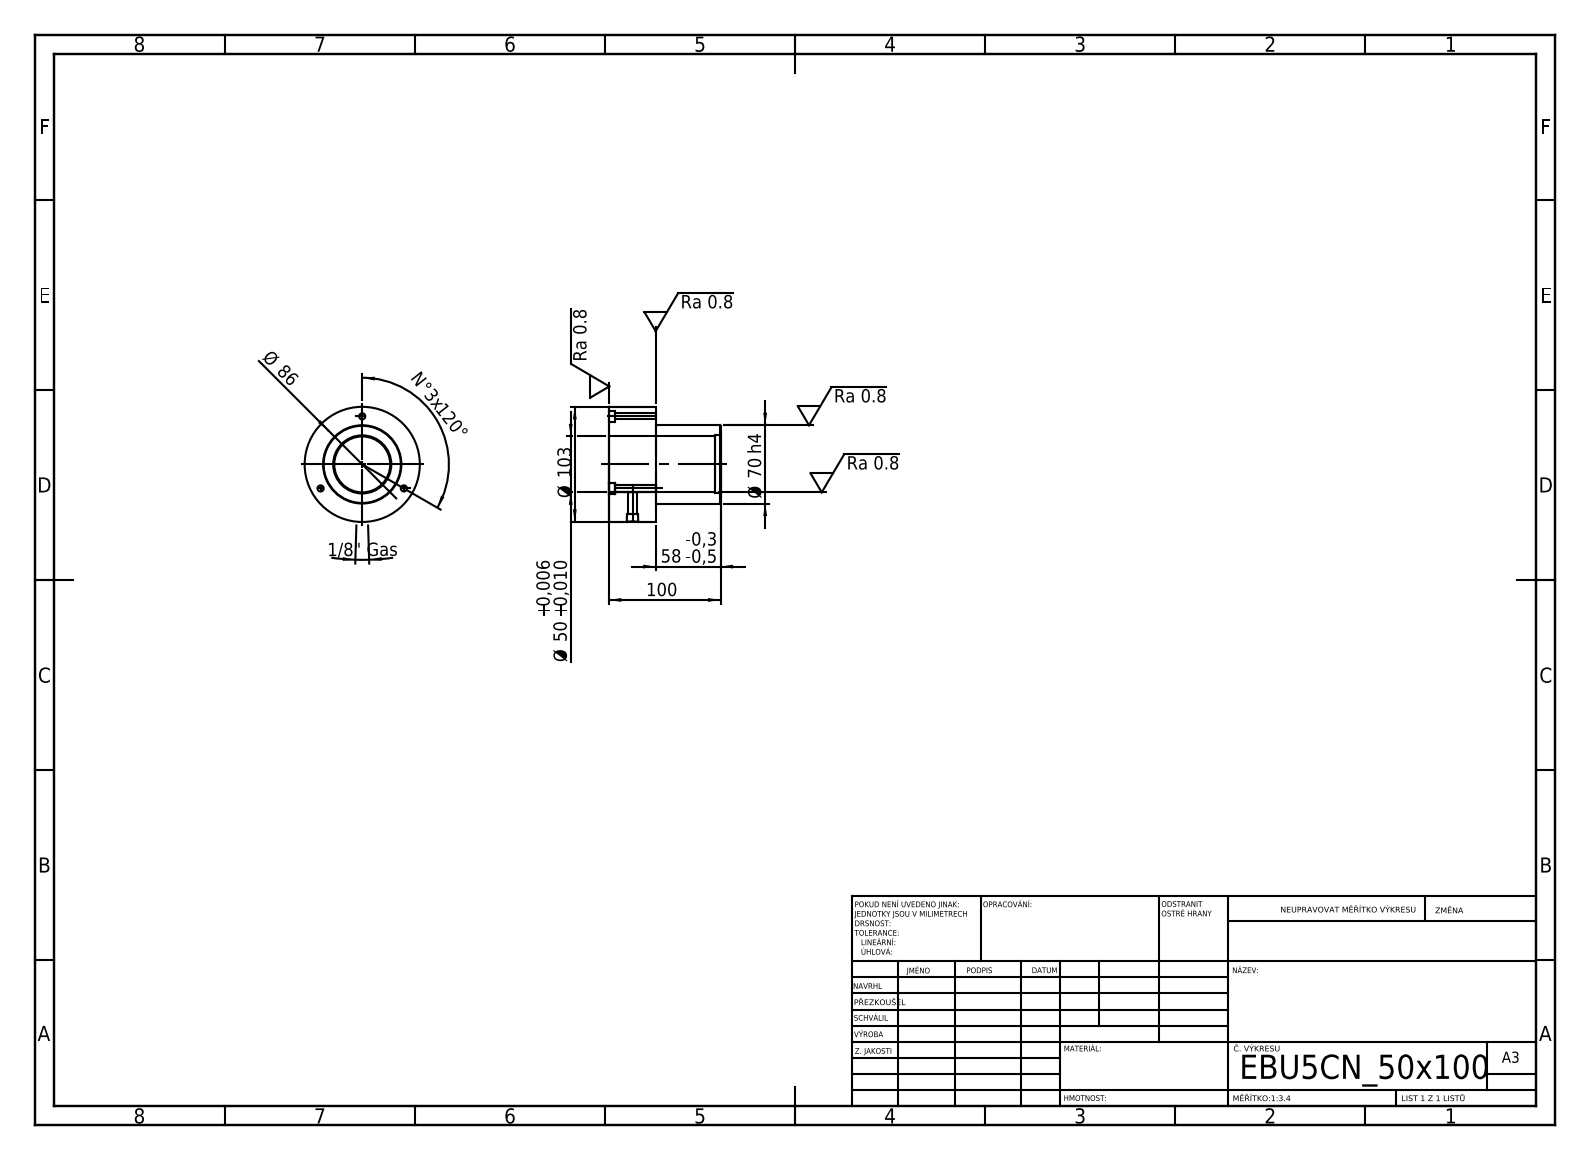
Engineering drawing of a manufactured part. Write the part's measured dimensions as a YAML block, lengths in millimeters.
step_written_by: "SolidWorks 2019 (CONFIG_CONTROL_DESIGN)"
units: millimeters
bodies: {solids: 1, faces: 36, planar: 8, cylindrical: 22, other: 6}
overall_size: [103, 103, 100]
volume: 370420
surface_area: 57546
round_holes:
  - {diameter: 5.5, count: 3}
  - {diameter: 10, count: 3}
  - {diameter: 8.43, count: 1}
  - {diameter: 50, count: 1}
  - {diameter: 52, count: 1}
round_bosses_or_shafts:
  - {diameter: 103, count: 1}
  - {diameter: 70, count: 1}
face_to_face_distances: [42, 58, 100, 94.6, 36.6, 5.4, 5, 53, 89.6, 95]
hole_center_spacings: [43, 74.48]
